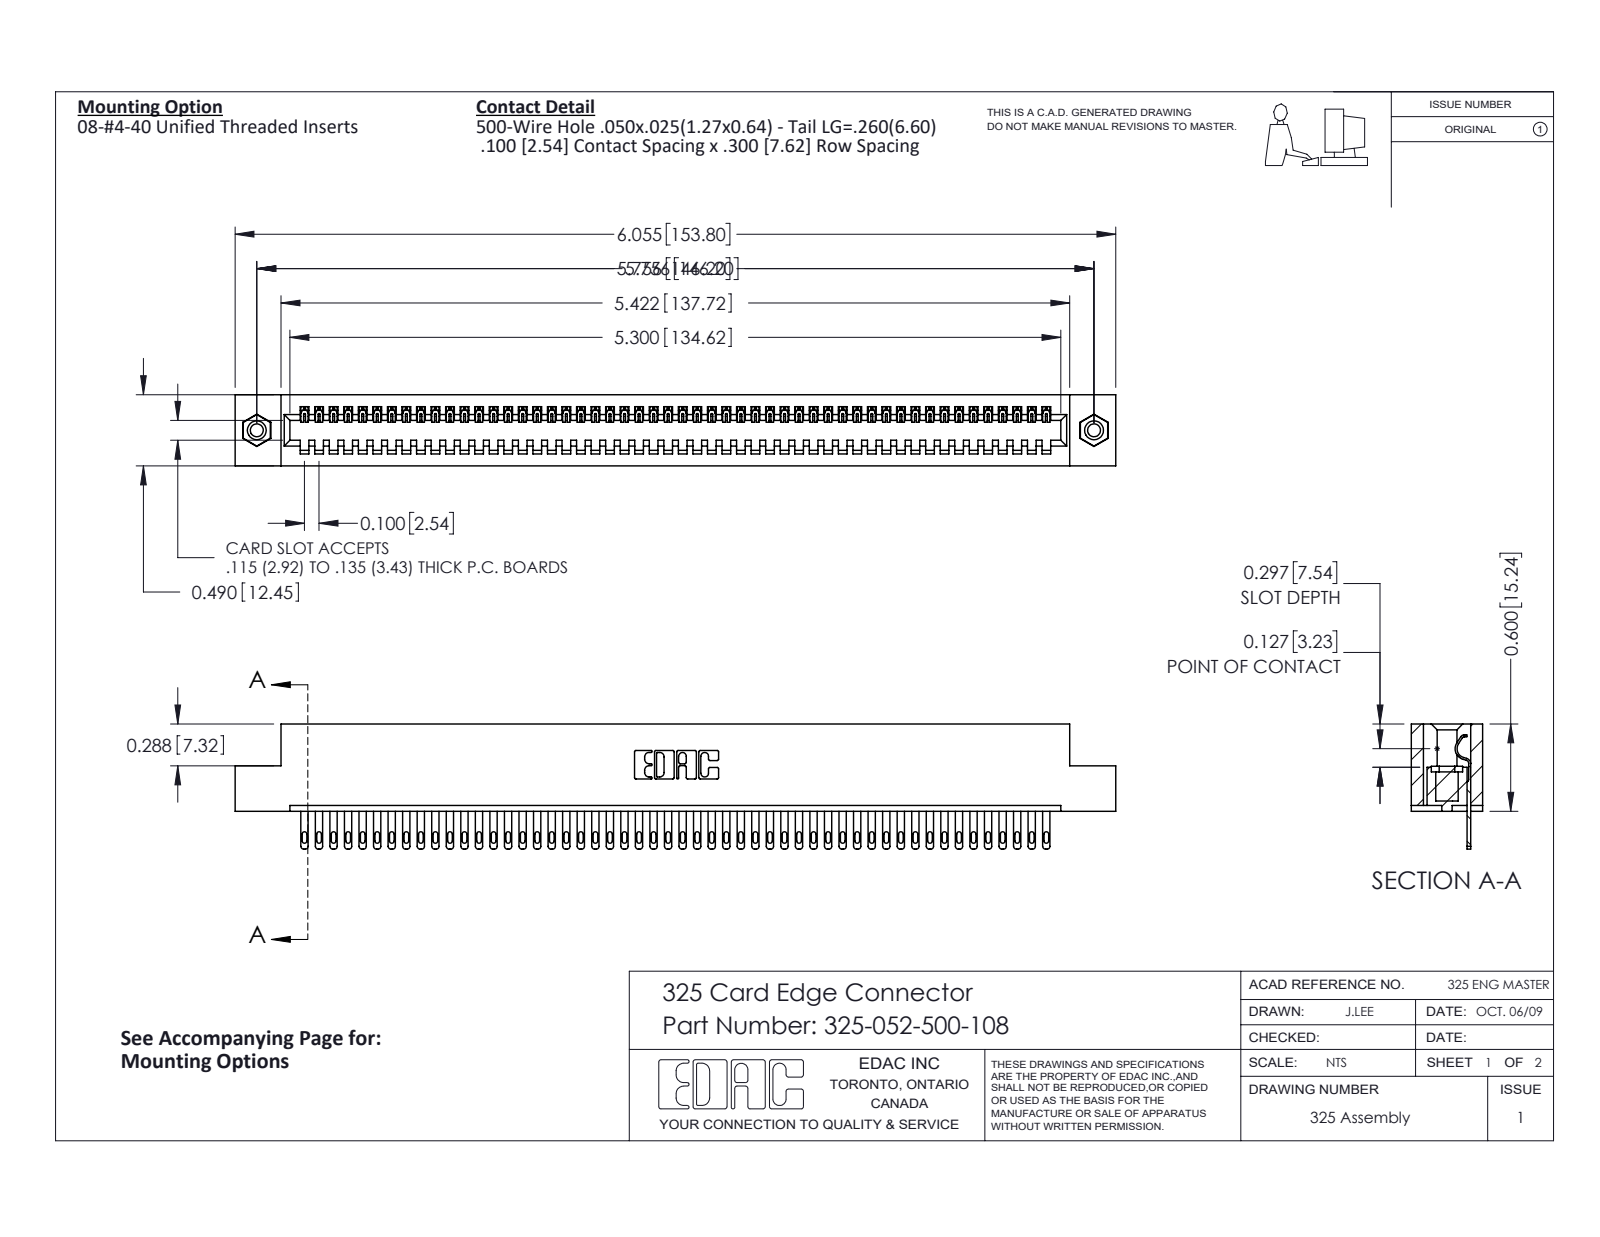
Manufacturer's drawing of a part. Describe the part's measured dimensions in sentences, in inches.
The part is named "325 Part_TI; 345-250-001_345-250-003-102; 325-292-001_325-293-100; 325-052-500-108". Its 3-D file was written by "SolidWorks 2016 (CONFIG_CONTROL_DESIGN)". It is 55 solids with 2982 faces: 1974 planar, 992 cylindrical and 16 other. Overall it measures 6.055 by 0.86 by 0.49 inches. Its volume is 1.198 cubic inches and its surface area 33.71 square inches. Round holes: 2 of diameter 0.089, 2 of diameter 0.125, 2 of diameter 0.16. Round bosses or shafts: 2 of diameter 0.155. Partial cylindrical surfaces (rounded edges, fillets, slot ends): 104 of radius 0.006, 104 of radius 0.016, 104 of radius 0.02, 22 of radius 0.01, 6 of radius 0.007, 6 of radius 0.031, 3 of radius 0.026, 1 of radius 0.014. The main face-to-face distances are 0.083, 0.407, 0.49, 0.3, 0.107, 0.383, 0.025, 0.325, 0.56, 0.263. The hole center spacings are 5.756.
